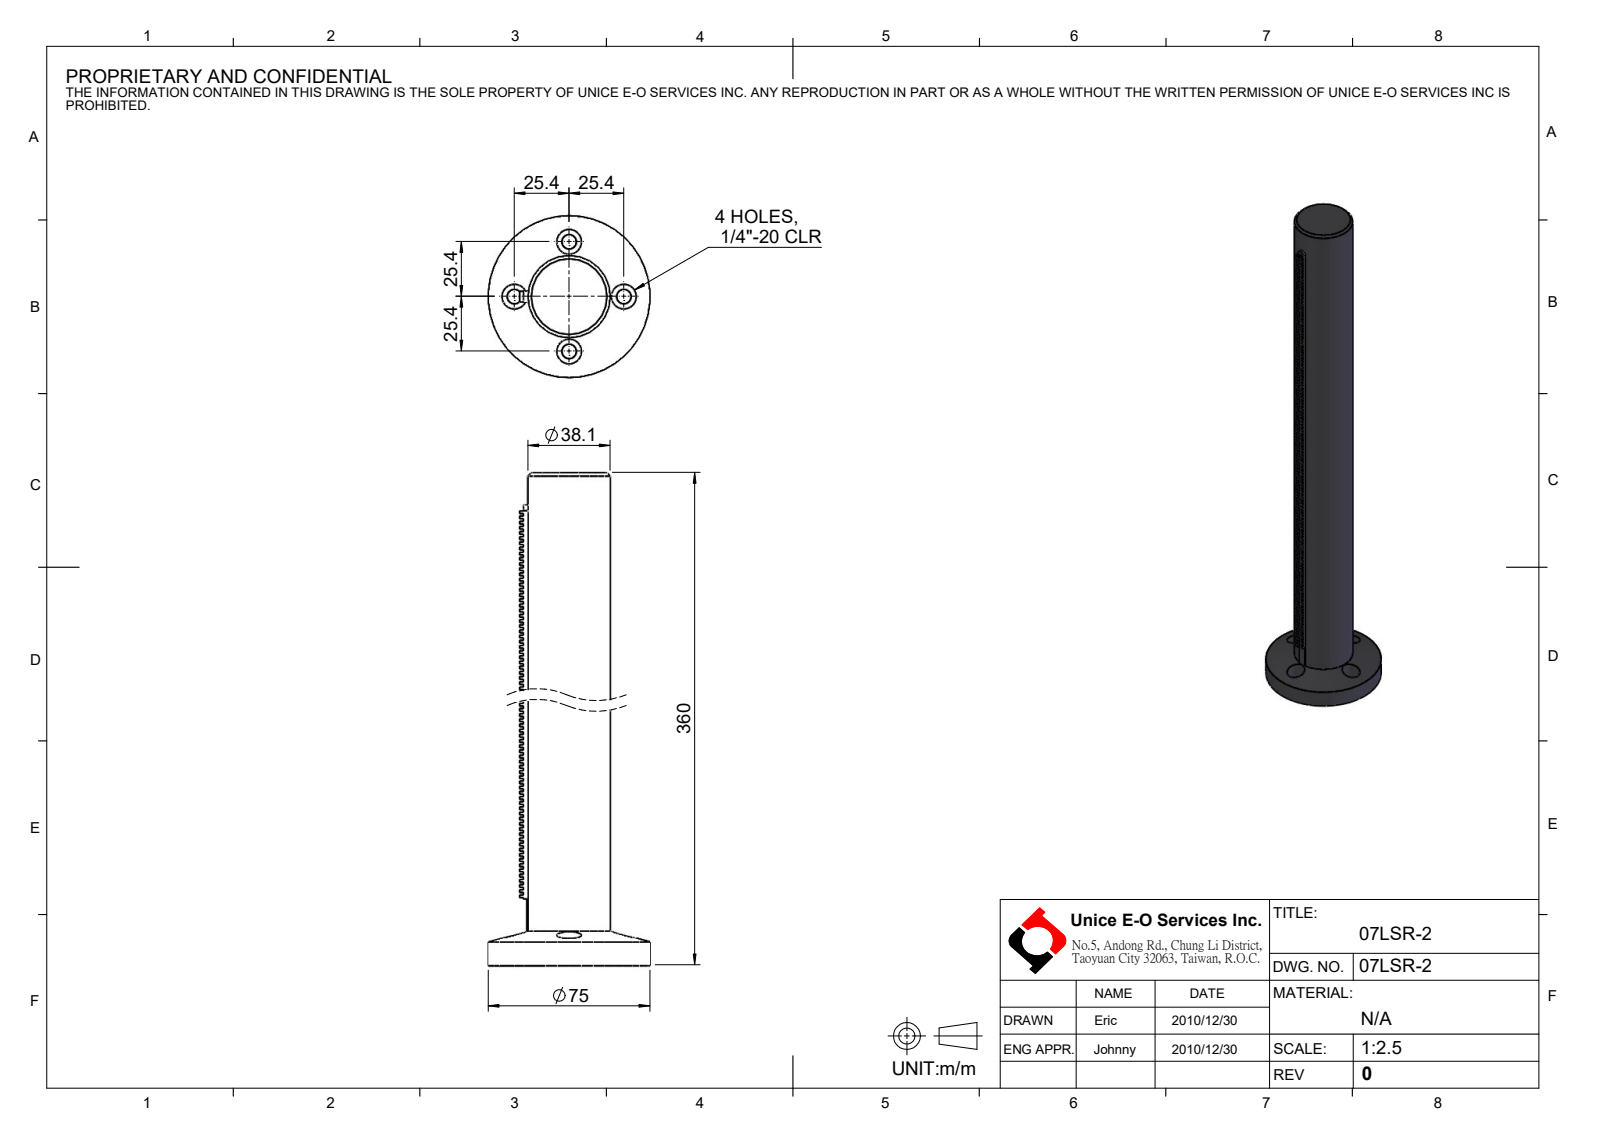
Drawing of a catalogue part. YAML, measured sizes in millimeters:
part_name: "07LSR-2"
step_written_by: "SolidWorks 2016 (CONFIG_CONTROL_DESIGN)"
units: millimeters
bodies: {solids: 3, faces: 595, planar: 551, cylindrical: 38, other: 6}
overall_size: [360, 75, 75]
volume: 451039
surface_area: 74945
round_holes:
  - {diameter: 6.76, count: 4}
  - {diameter: 11.51, count: 4}
  - {diameter: 5, count: 1}
  - {diameter: 6.6, count: 1}
  - {diameter: 11, count: 1}
  - {diameter: 25, count: 1}
round_bosses_or_shafts:
  - {diameter: 75, count: 1}
  - {diameter: 38.1, count: 1}
partial_cylinders:
  - {radius: 2.5, count: 1}
  - {radius: 3.95, count: 1}
  - {radius: 5.25, count: 1}
face_to_face_distances: [1.6, 5, 16, 1.45, 6.45, 1.3, 2.75, 7.75, 9.2, 360]
hole_center_spacings: [25.4, 35.92, 50.8]
